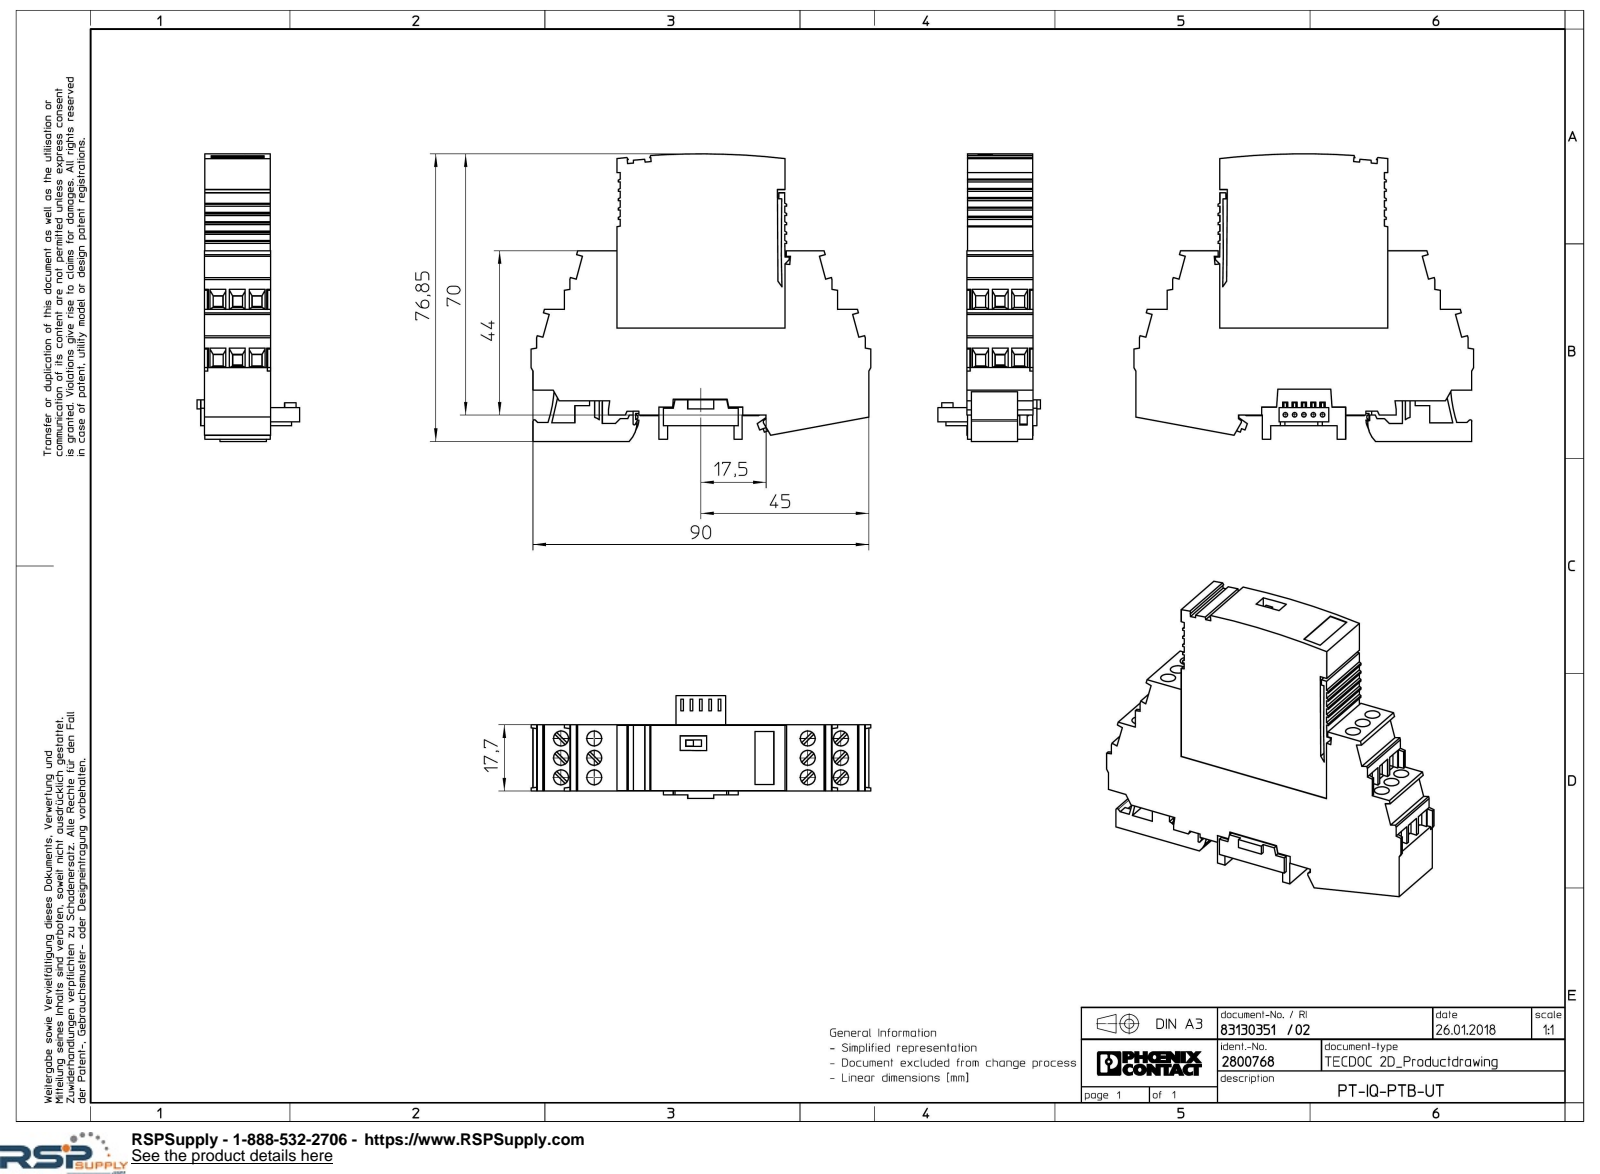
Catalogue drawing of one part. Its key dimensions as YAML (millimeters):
part_name: "PT_IQ_PTB_UT-select"
step_written_by: "Creo Elements/Direct Modeling 20.1A 29-Sep-2018 (C) Parametric Technology GmbH (AUTOMOTIVE_DESIGN)"
units: millimeters
bodies: {solids: 1, faces: 698, planar: 650, cylindrical: 43, other: 5}
overall_size: [91.05, 76.85, 27.48]
volume: 83989
surface_area: 21078
round_holes:
  - {diameter: 4, count: 12}
  - {diameter: 1.2, count: 5}
partial_cylinders:
  - {radius: 0.3, count: 1}
  - {radius: 0.4, count: 1}
  - {radius: 4, count: 1}
  - {radius: 9.5, count: 1}
  - {radius: 36.42, count: 1}
  - {radius: 200, count: 1}
face_to_face_distances: [17.69, 17.59, 17.5, 17.6, 4.15, 67.5, 22.5, 3.8, 50.98, 46.83]
hole_center_spacings: [5.2, 10.31, 66.3, 8.9, 66.1, 2.5, 10.4, 13.69]
